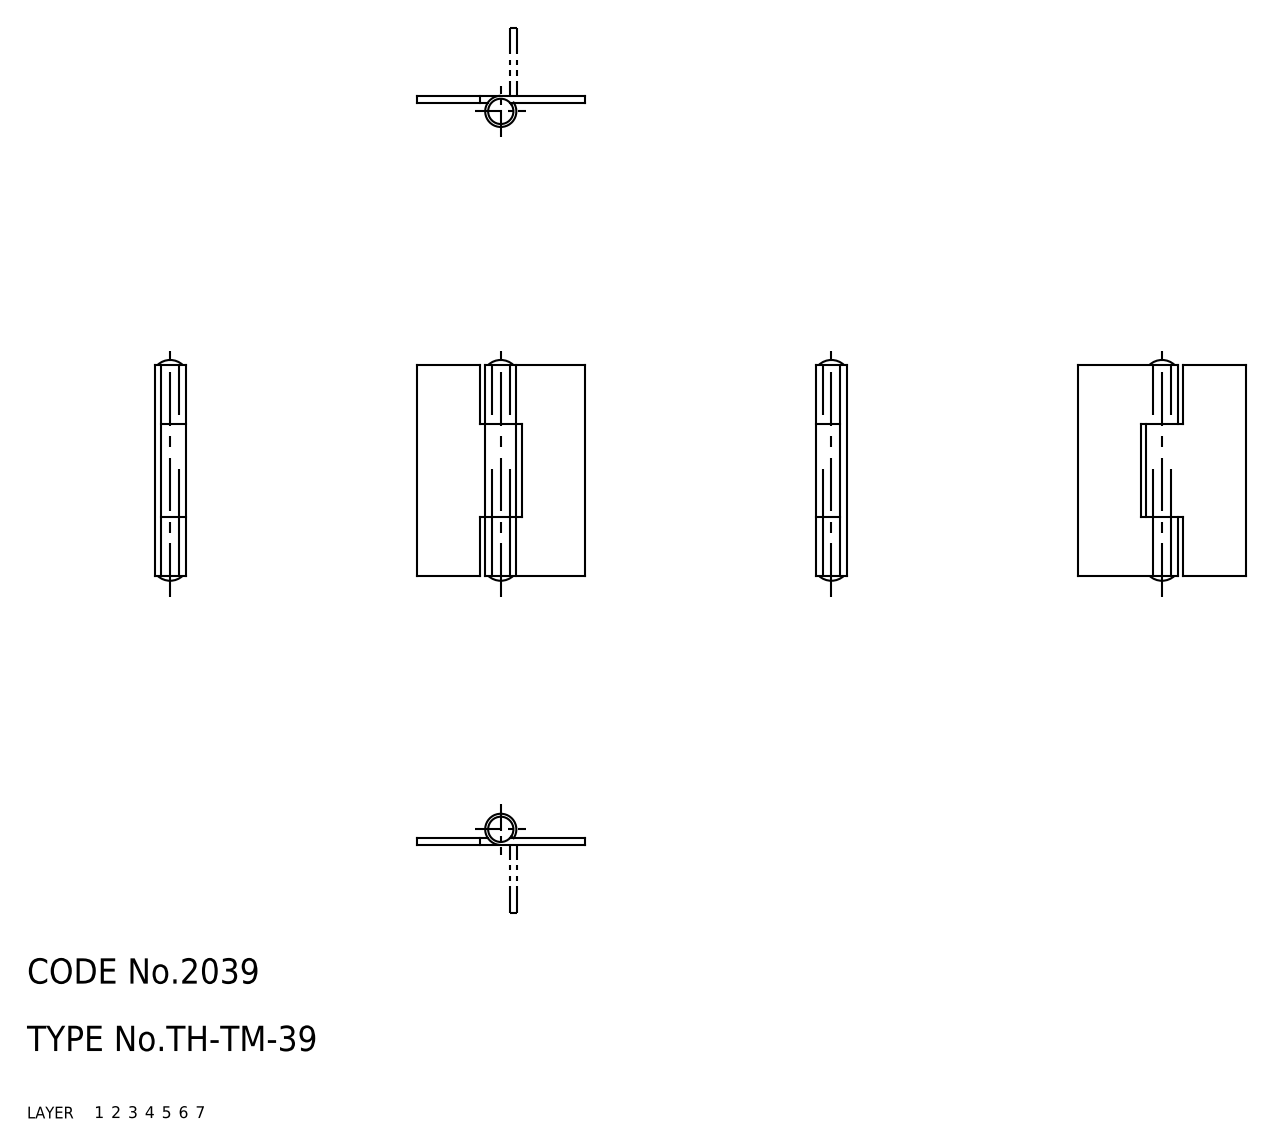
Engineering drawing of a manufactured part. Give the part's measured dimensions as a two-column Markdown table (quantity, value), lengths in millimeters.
| quantity | value |
| --- | --- |
| part name | 67110784; 67110797; 67110810 |
| STEP written by | CADfix (AUTOMOTIVE_DESIGN) |
| units | millimeters |
| bodies | 3 solids, 32 faces (0 planar, 0 cylindrical, 32 other) |
| overall size | 26.2 × 20 × 3.7 |
| volume | 594 mm³ |
| surface area | 1 600 mm² |
